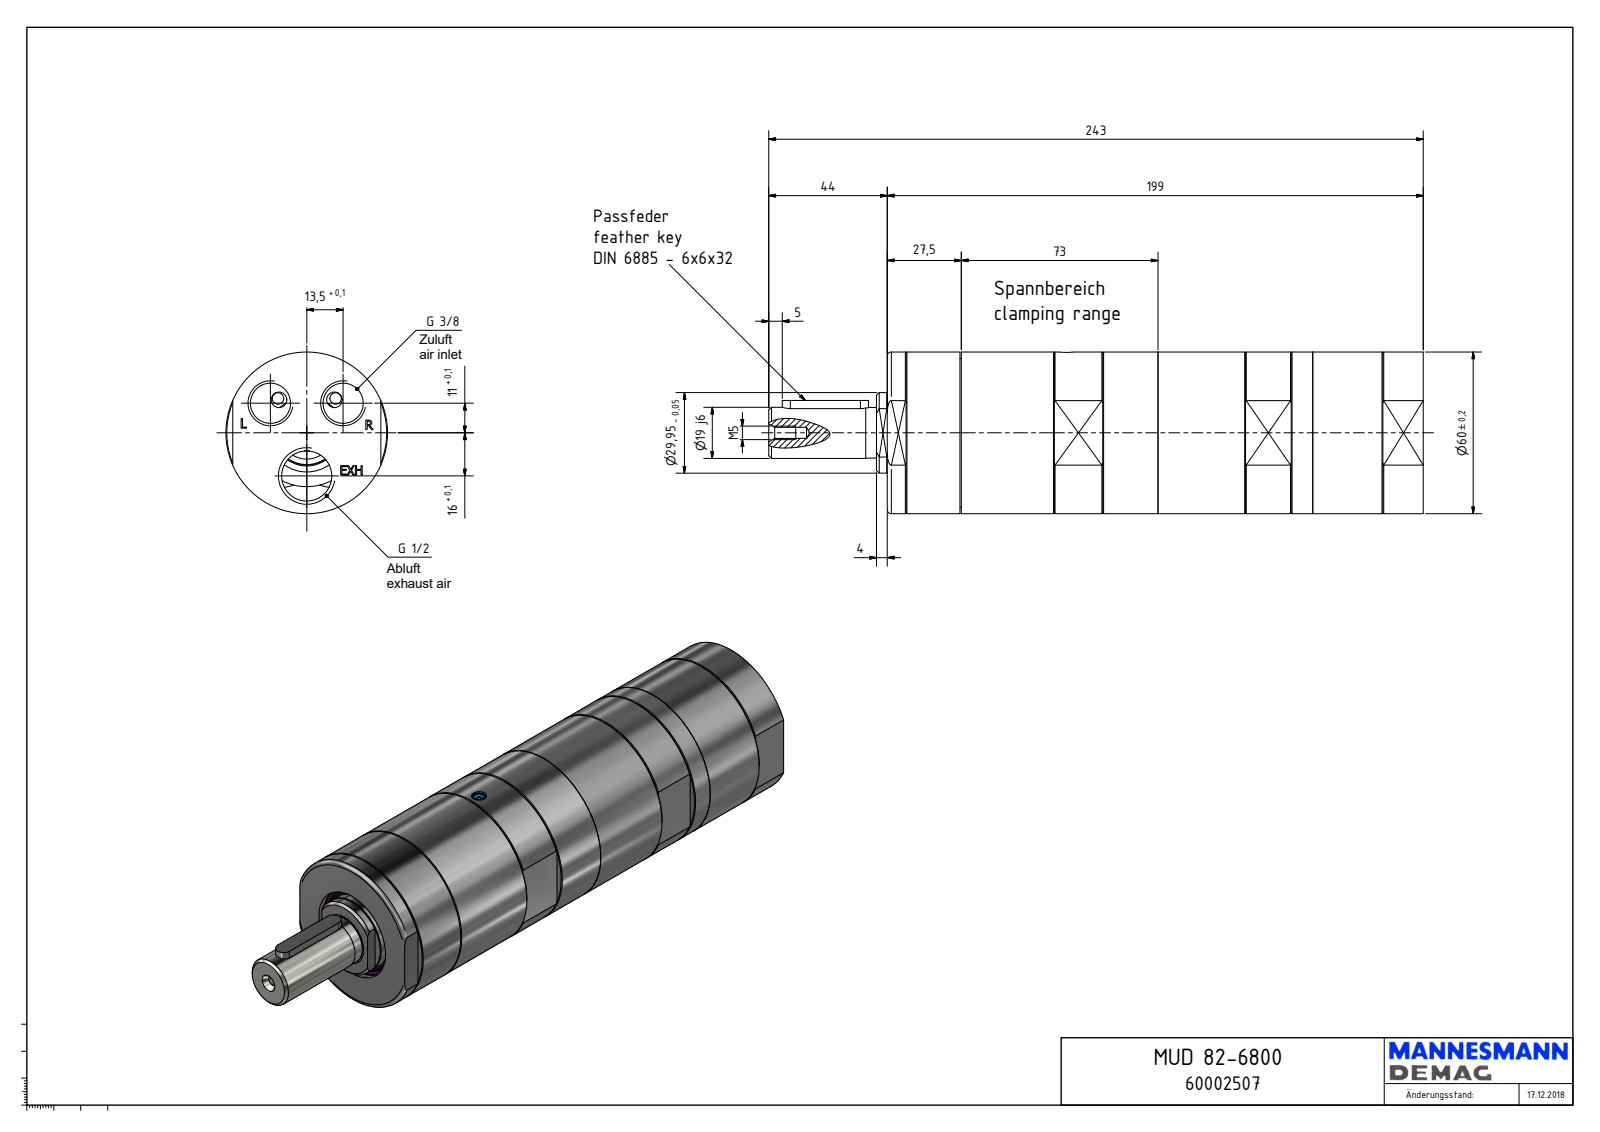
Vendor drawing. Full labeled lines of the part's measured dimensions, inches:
Part name (STEP PRODUCT): MUD 82-6800_60002507
STEP written by: Autodesk Inventor 2018 (AUTOMOTIVE_DESIGN)
Units: inches
Bodies: 1 solid, 492 faces (206 planar, 240 cylindrical, 46 other)
Overall size (bounding box): 9.567 × 2.362 × 2.362
Volume: 34.17 in³ · Surface area: 86.62 in²
Round holes (diameter × count): ⌀0.589 ×2, ⌀0.061 ×1, ⌀0.157 ×1, ⌀0.163 ×1, ⌀0.217 ×1, ⌀0.733 ×1, ⌀1.378 ×1, ⌀2.18 ×1
Round bosses / shafts (diameter × count): ⌀2.362 ×1, ⌀2.172 ×1, ⌀1.179 ×1, ⌀0.748 ×1, ⌀0.74 ×1, ⌀0.197 ×1, ⌀0.142 ×1, ⌀0.13 ×1
Partial cylindrical surfaces — rounded edges, fillets, slot ends (radius × count): R0.46 ×94, R0.118 ×2, R0.295 ×2, R0.748 ×1, R0.925 ×1, R0.948 ×1, R0.983 ×1, R1.087 ×1
Main face-to-face distances: 7.835, 2.165, 1.083, 6.752, 7.43, 6.347, 0.405, 0.157, 6.988, 5.905
Hole centre spacings: 0.685, 1.189, 0.63, 1.063
